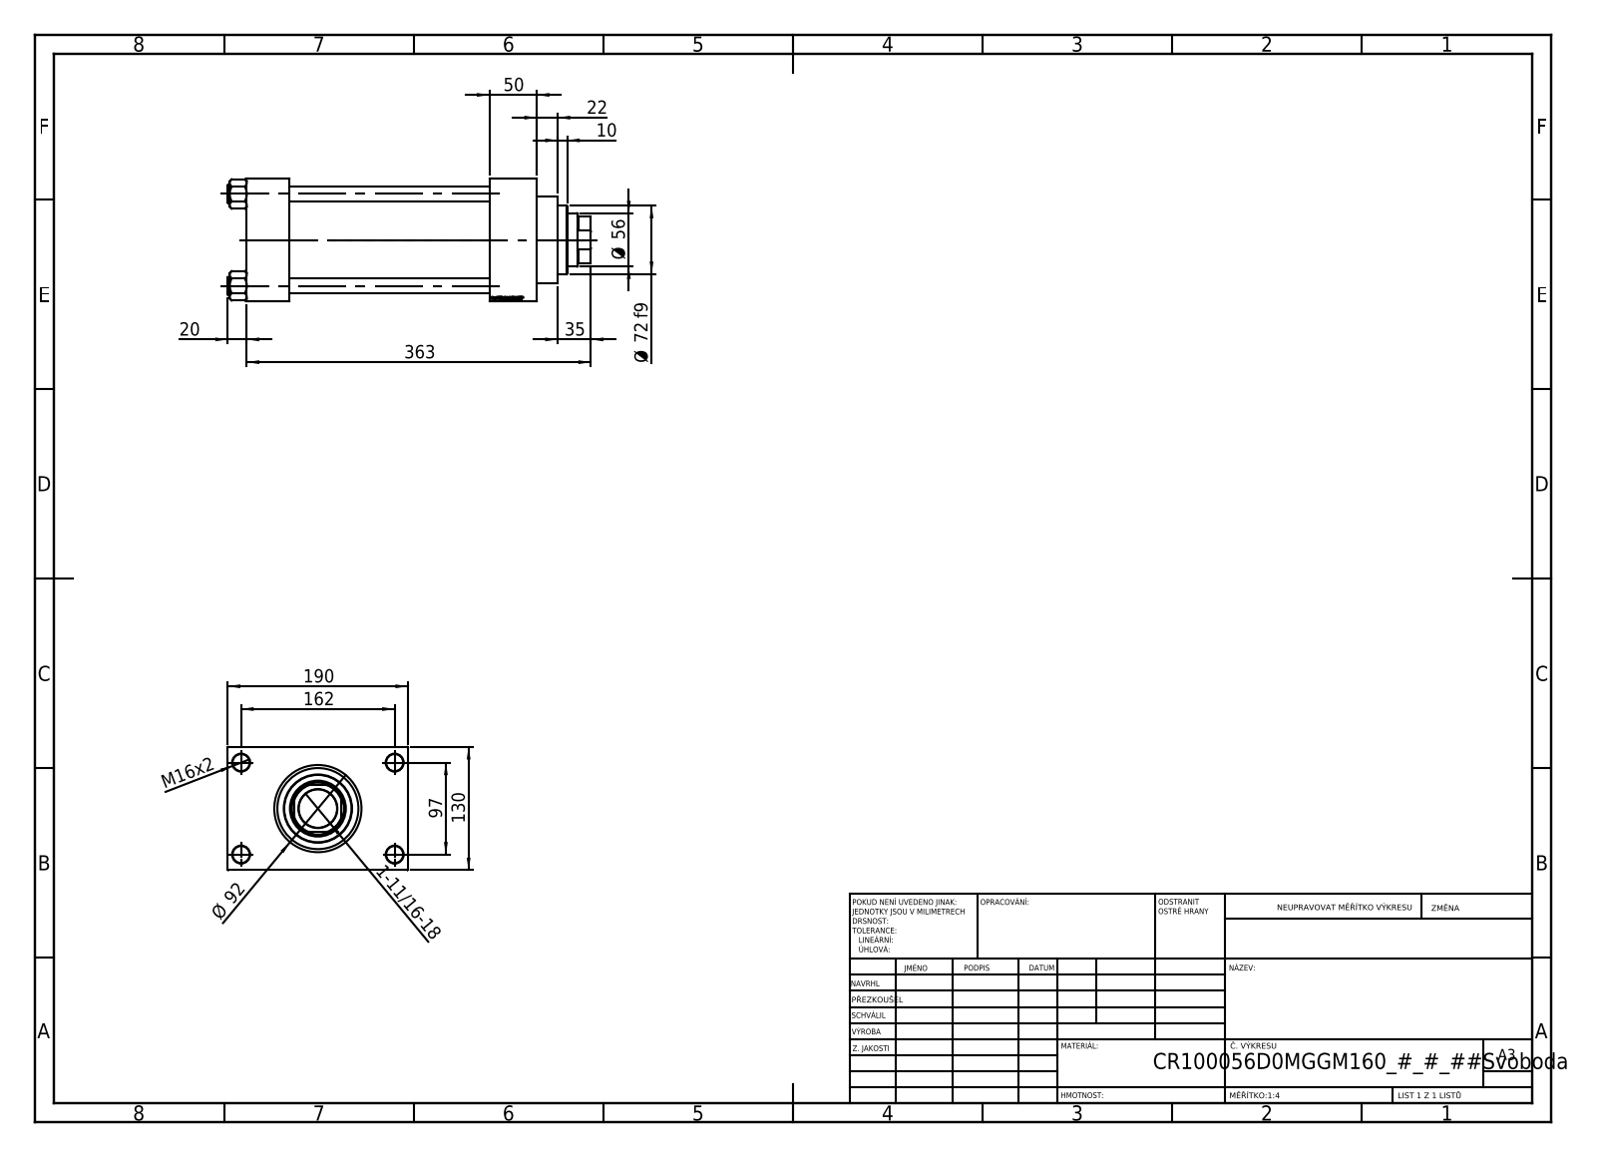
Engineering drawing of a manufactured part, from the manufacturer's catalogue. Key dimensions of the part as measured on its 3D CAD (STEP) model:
Part name (STEP PRODUCT): V215CR_D_TYCINKA; NUT_M5_D; V215CR_VCP_D; V215_VC_A (+1 more)
STEP written by: SolidWorks 2019 (CONFIG_CONTROL_DESIGN)
Units: millimetres
Bodies: 11 solids, 1152 faces (545 planar, 89 cylindrical, 518 other)
Overall size (bounding box): 383 × 190 × 130
Volume: 3 238 000 mm³ · Surface area: 503 262 mm²
Round holes (diameter × count): ⌀16 ×4, ⌀18 ×4, ⌀7 ×2, ⌀26.44 ×2, ⌀35 ×2, ⌀40.5 ×1, ⌀56 ×1, ⌀59 ×1, ⌀76 ×1, ⌀85.5 ×1, ⌀100 ×1
Round bosses / shafts (diameter × count): ⌀19 ×4, ⌀106 ×1, ⌀92 ×1, ⌀72 ×1
Partial cylindrical surfaces — rounded edges, fillets, slot ends (radius × count): R27 ×1
Main face-to-face distances: 130, 50, 45, 256, 211, 160, 306, 261, 30, 190
Hole centre spacings: 32.55, 68.52, 94.41, 96.9, 102.27, 129.45, 161.73, 97
